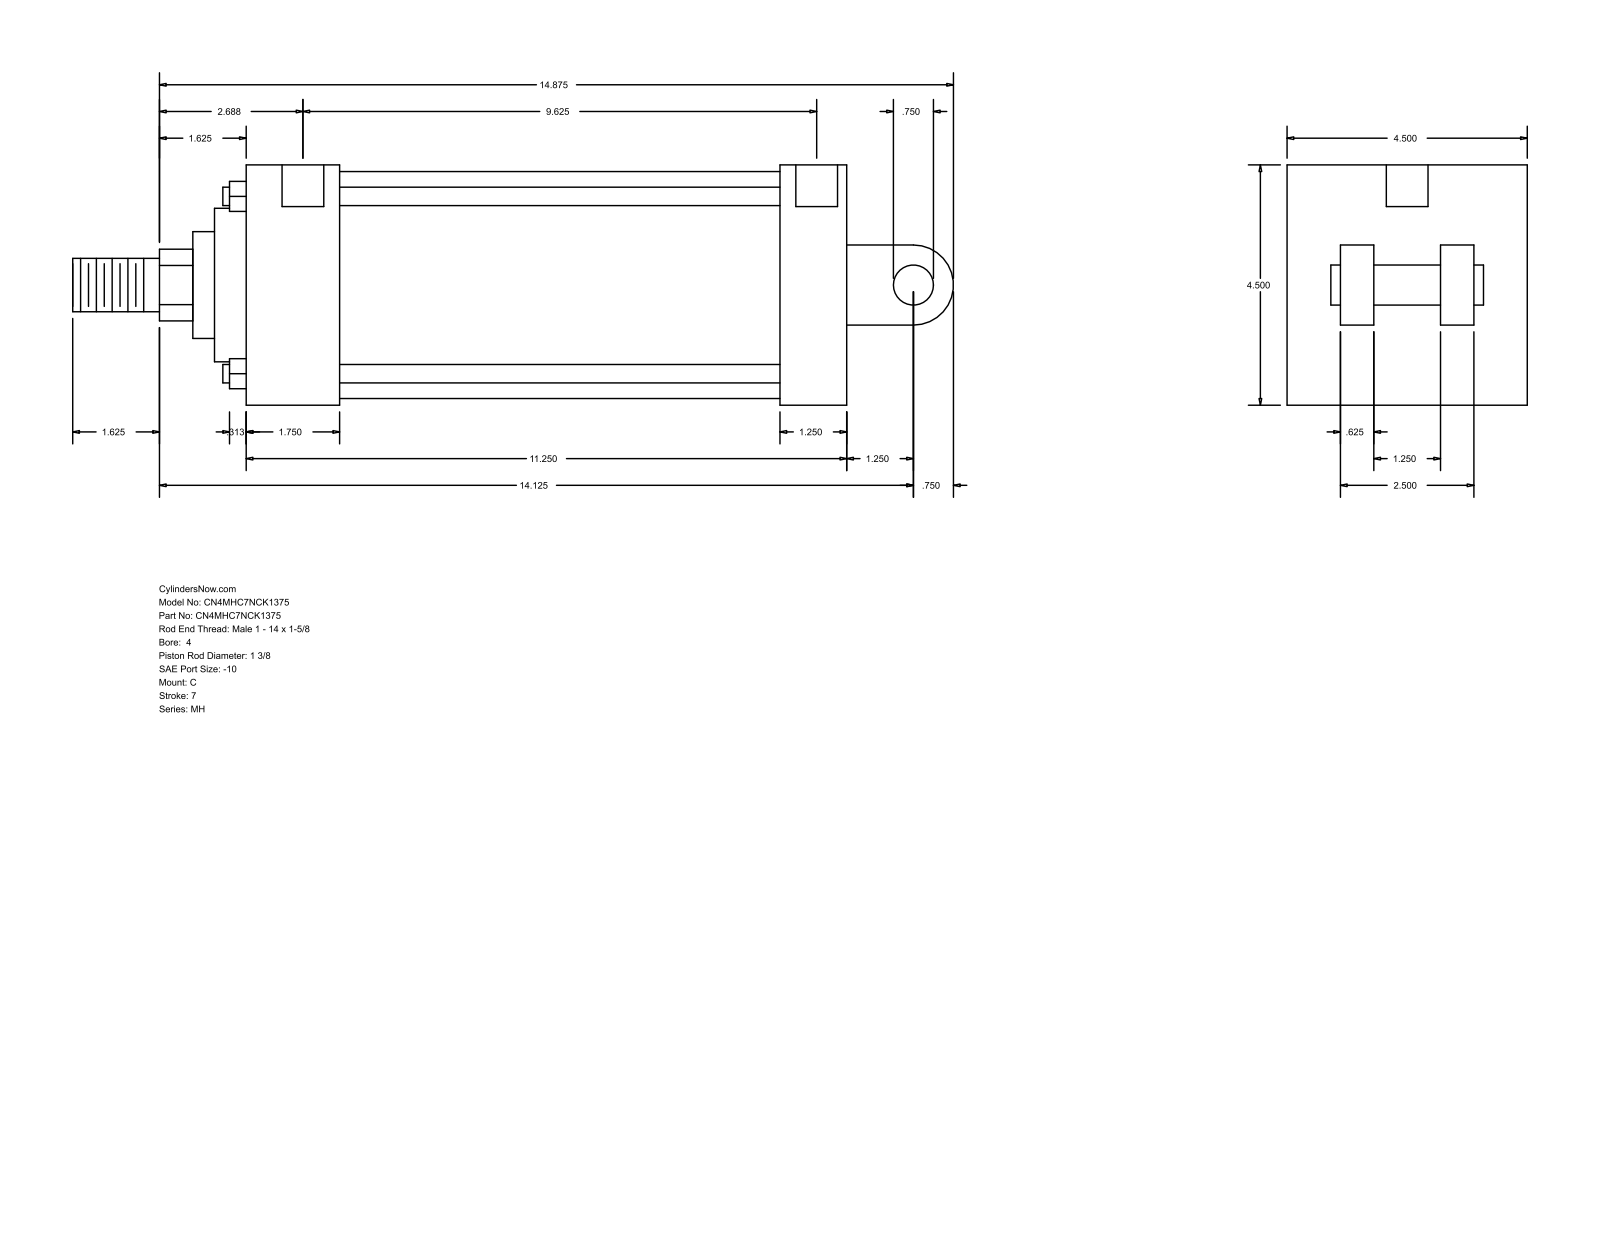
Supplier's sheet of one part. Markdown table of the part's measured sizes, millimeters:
| quantity | value |
| --- | --- |
| part name | MH_C__0400_1.375 |
| STEP written by | GSSL Pune (CONFIG_CONTROL_DESIGN) |
| units | millimeters |
| bodies | 0 solids, 101 faces (71 planar, 30 cylindrical, 0 other) |
| overall size | 419.1 × 114.3 × 114.3 |
| round holes (diameter × count) | 8.73 × 4, 19.84 × 2 |
| round bosses / shafts (diameter × count) | 8.76 × 4, 107.95 × 1, 73.03 × 1, 50.8 × 1, 34.92 × 1, 25.4 × 1, 19.05 × 1 |
| partial cylindrical surfaces (radius × count) | 17.06 × 1, 19.05 × 1 |
| main face-to-face distances | 114.3, 285.75, 44.45, 254, 209.55, 241.3, 31.75, 41.27, 73.03, 38.1 |
| hole center spacings | 247.65, 1.58, 1.59, 244.48, 246.06, 246.07 |
